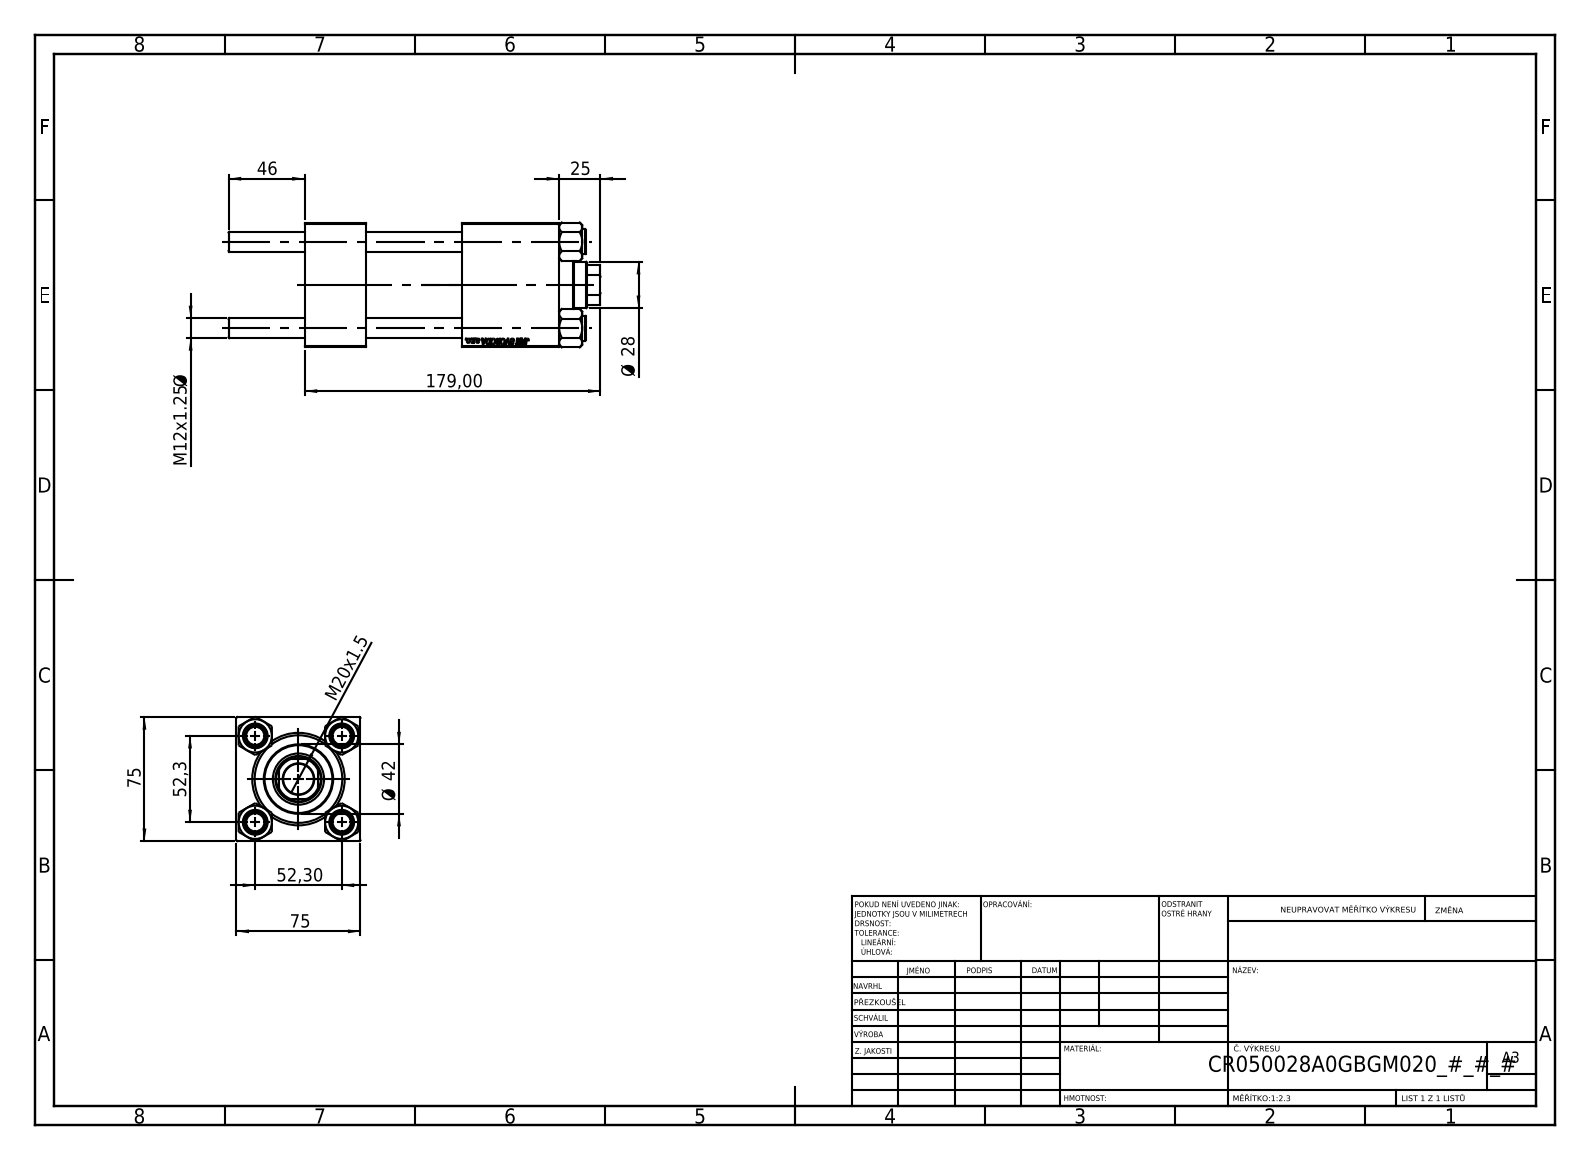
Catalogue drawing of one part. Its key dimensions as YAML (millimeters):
part_name: "CR025_012_A_0_G_A_G_M_020_+#_##_TYCINKA; V215_VC_A; V215CR_BODY_A; V215CR_VCP (+1 more)"
step_written_by: "SolidWorks 2019 (CONFIG_CONTROL_DESIGN)"
units: millimeters
bodies: {solids: 11, faces: 1133, planar: 519, cylindrical: 78, other: 536}
overall_size: [225, 75.54, 75]
volume: 702024
surface_area: 167528
round_holes:
  - {diameter: 12, count: 4}
  - {diameter: 7, count: 2}
  - {diameter: 20.96, count: 2}
  - {diameter: 30, count: 2}
  - {diameter: 18.5, count: 1}
  - {diameter: 28, count: 1}
  - {diameter: 31, count: 1}
  - {diameter: 41, count: 1}
  - {diameter: 50, count: 1}
  - {diameter: 53, count: 1}
round_bosses_or_shafts:
  - {diameter: 15, count: 4}
  - {diameter: 56, count: 1}
  - {diameter: 42, count: 1}
partial_cylinders:
  - {radius: 13.5, count: 1}
face_to_face_distances: [75, 37, 154, 117, 95, 58, 59, 125.3, 88.3, 30.3]
hole_center_spacings: [36.98, 52.3, 73.96, 93.5]
